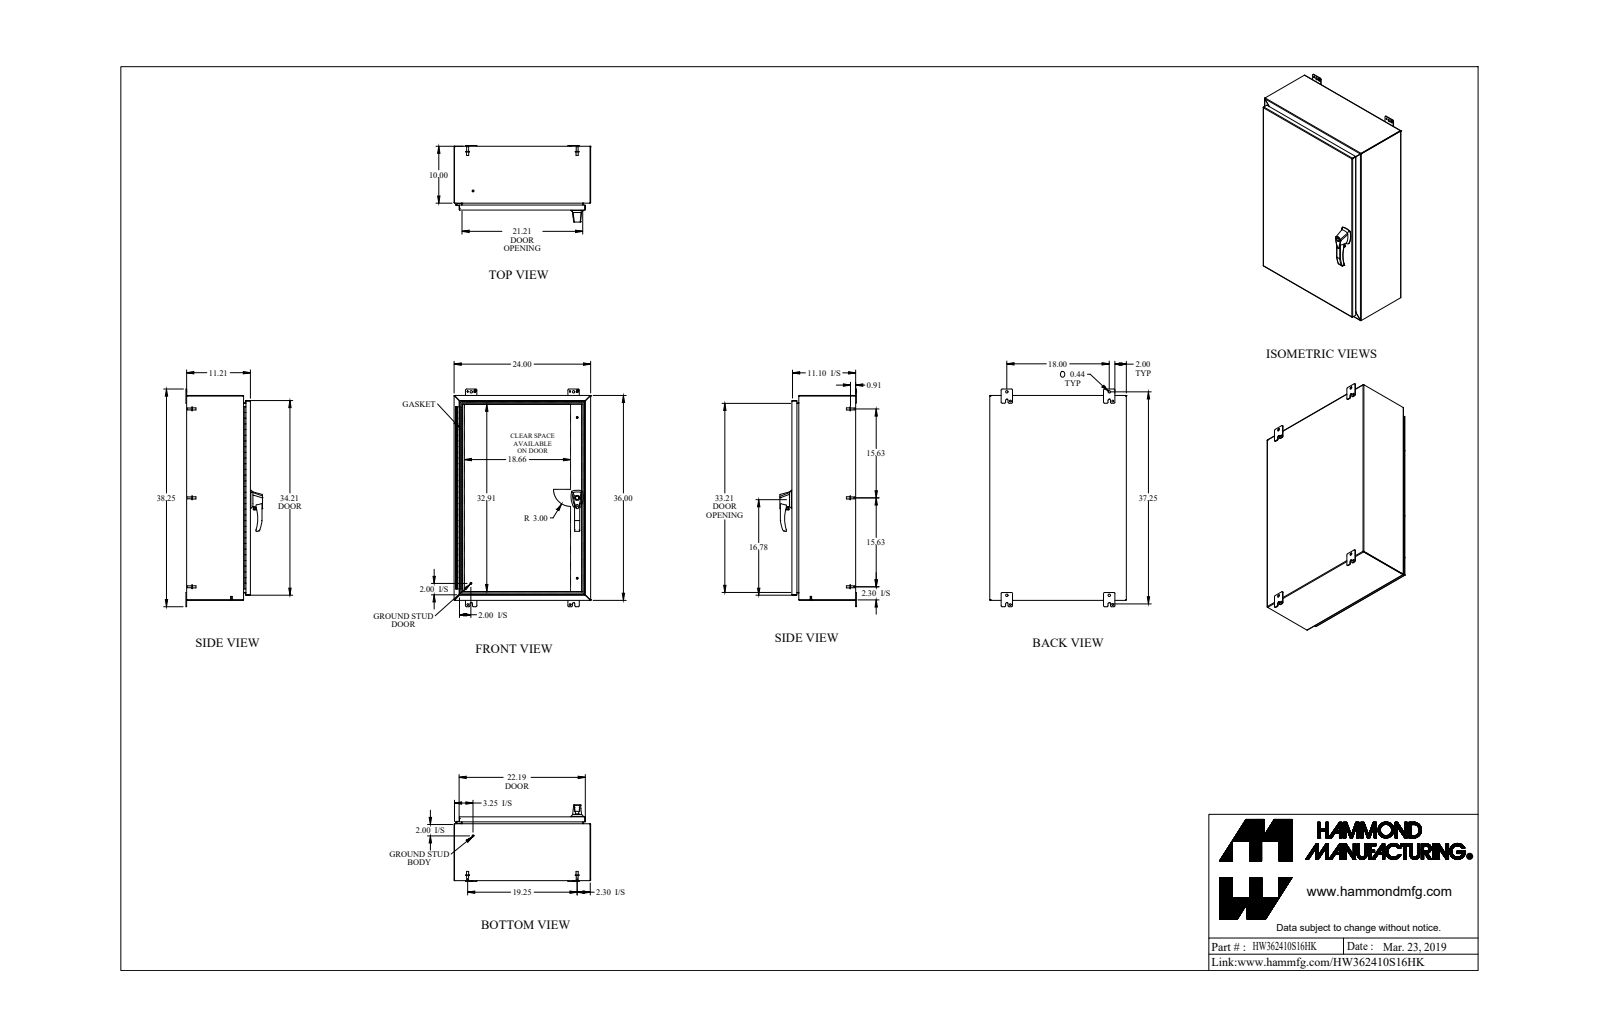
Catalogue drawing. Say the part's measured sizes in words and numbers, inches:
The part is named "HW362410S16HK". Its 3-D file was written by "SolidWorks 2018 (AUTOMOTIVE_DESIGN)". It is 44 solids with 1542 faces: 720 planar, 658 cylindrical and 164 other. Overall it measures 38.25 by 24 by 13.45 inches. Its volume is 269.3 cubic inches and its surface area 7 055 square inches. Round holes: 6 of diameter 0.176, 5 of diameter 0.313, 3 of diameter 0.25, 3 of diameter 0.265, 3 of diameter 0.413, 2 of diameter 0.196, 2 of diameter 0.256, 2 of diameter 0.394, 2 of diameter 0.437, 1 of diameter 0.11, 1 of diameter 0.233, 1 of diameter 0.33. Round bosses or shafts: 11 of diameter 0.375, 7 of diameter 0.25, 6 of diameter 0.65, 6 of diameter 0.332, 6 of diameter 0.156, 3 of diameter 1, 3 of diameter 0.51, 2 of diameter 0.63. Partial cylindrical surfaces (rounded edges, fillets, slot ends): 27 of radius 0.25, 23 of radius 0.188, 20 of radius 0.036, 20 of radius 0.108, 12 of radius 0.06, 9 of radius 0.125, 8 of radius 0.045, 8 of radius 0.218. The main face-to-face distances are 0.072, 11.138, 11.066, 0.072, 11.138, 11.21, 23.928, 35.928, 23.856, 24. The hole center spacings are 1.11, 14.118, 14.119, 28.237, 10.37, 14.119, 18, 37.38.
